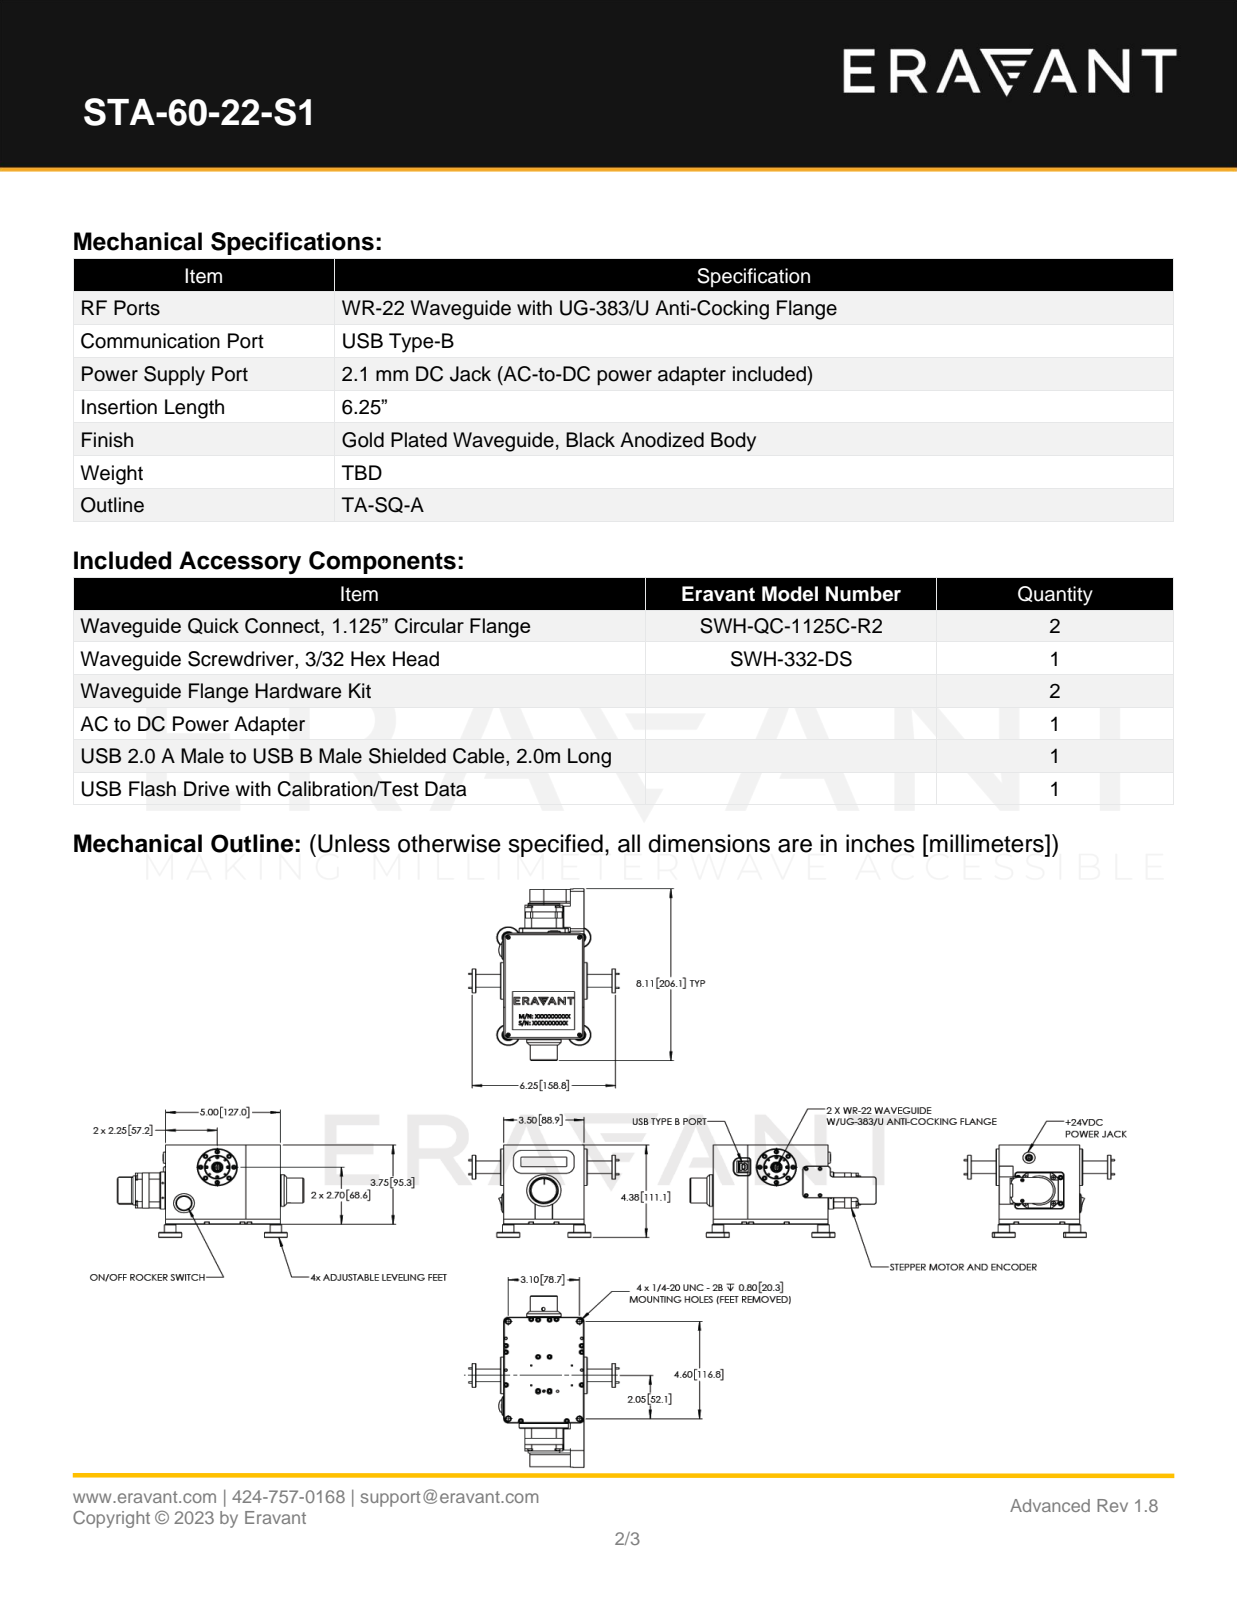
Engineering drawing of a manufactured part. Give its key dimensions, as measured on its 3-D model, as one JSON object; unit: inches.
{"part_name": "STA-60-22-S1", "step_written_by": "SolidWorks 2021 (CONFIG_CONTROL_DESIGN)", "units": "inches", "bodies": {"solids": 59, "faces": 3082, "planar": 1333, "cylindrical": 891, "other": 858}, "overall_size": [8.114, 6.555, 4.375], "volume_in3": 35.29, "surface_area_in2": 338.9, "round_holes": [[0.089, 20], [0.07, 18], [0.129, 18], [0.096, 12], [0.2, 9], [0.219, 8], [0.061, 4], [0.067, 4], [0.097, 4], [0.118, 4], [0.14, 4], [0.144, 4]], "round_bosses_or_shafts": [[0.183, 29], [0.112, 24], [0.086, 8], [0.5, 5], [1, 4], [0.25, 4], [0.205, 4], [0.14, 4]], "partial_cylinders_radius": [[0.012, 44], [0.25, 24], [0.024, 14], [0.109, 14], [0.15, 14], [0.125, 13], [0.158, 8], [0.015, 6]], "face_to_face_distances": [3.5, 0.25, 0.2, 3.3, 3.75, 3.437, 0.063, 3.687, 5, 3.1], "hole_center_spacings": [0.515, 1.107, 0.863, 1.025, 0.359, 0.469, 0.663, 0.866]}
